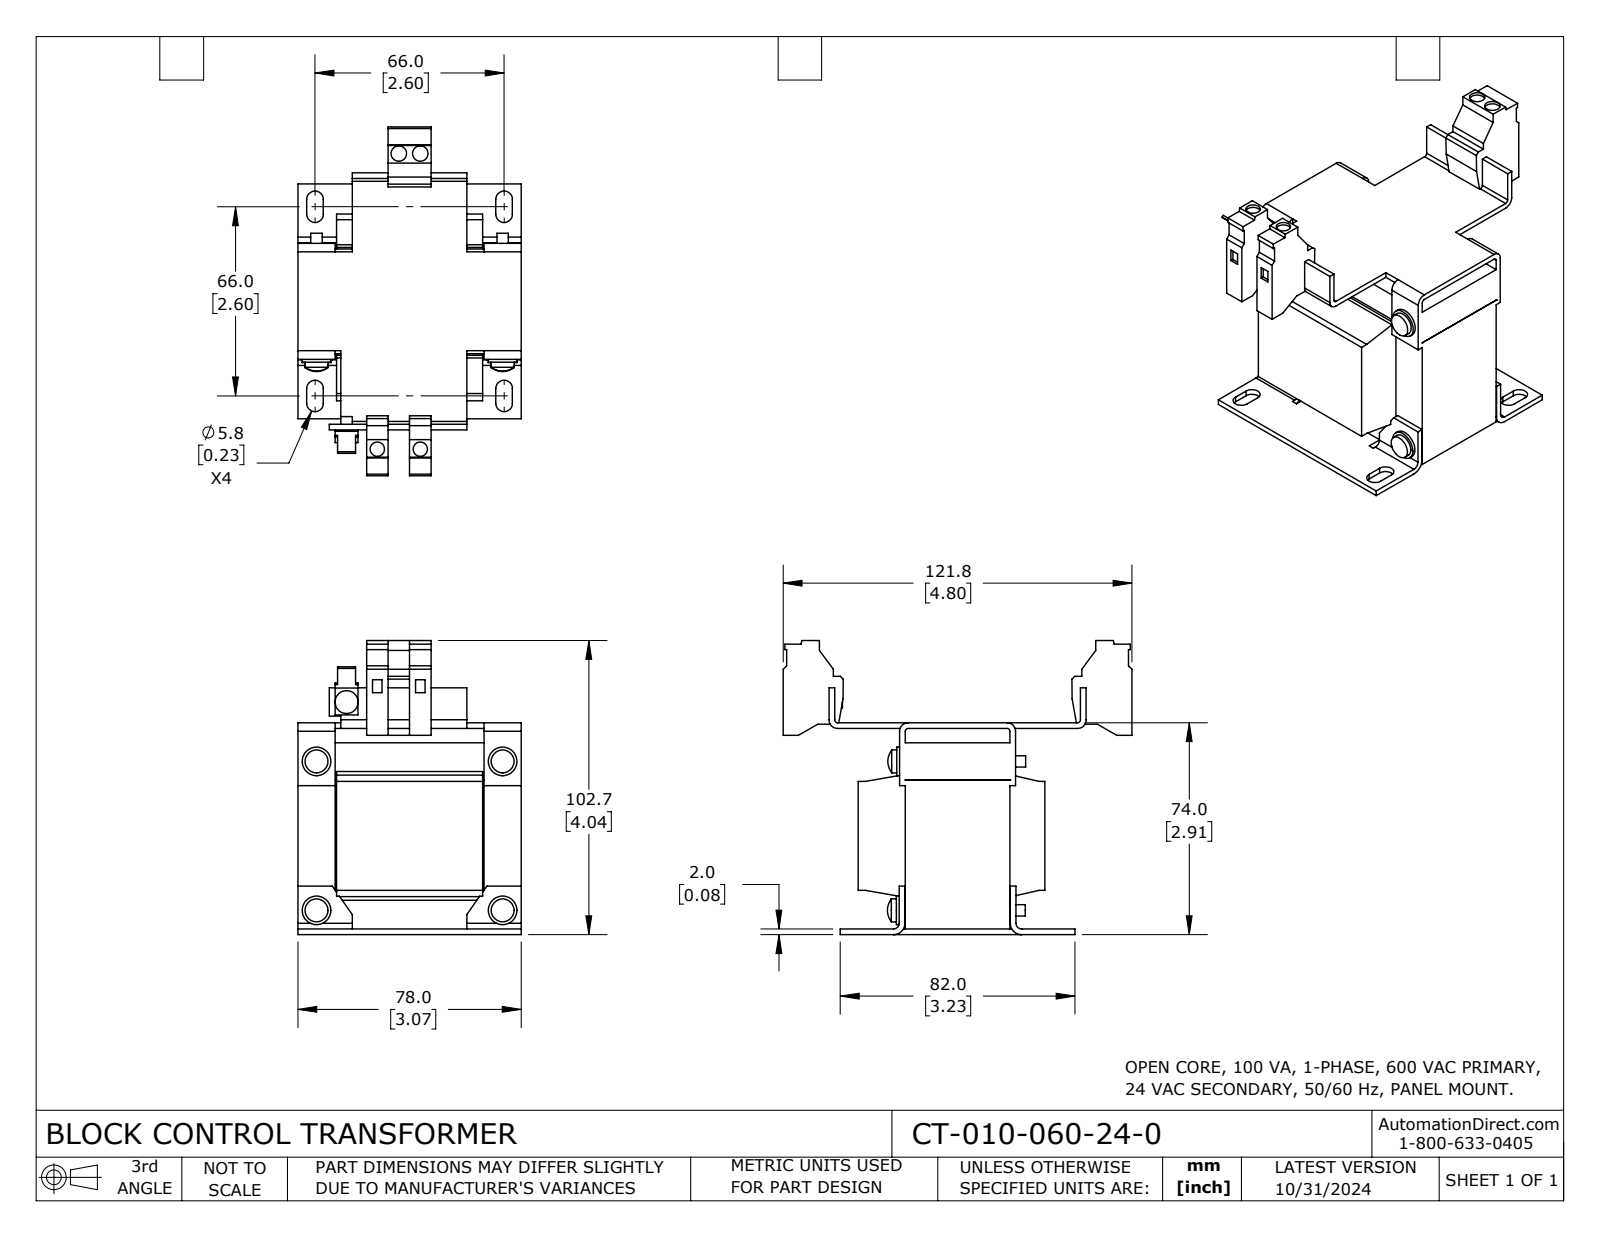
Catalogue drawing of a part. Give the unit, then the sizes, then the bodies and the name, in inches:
Units: inches
Overall size (bounding box): 4.795 × 4.043 × 3.071
Round holes (diameter × count): ⌀0.197 ×2, ⌀0.213 ×2
Round bosses / shafts (diameter × count): ⌀0.315 ×5, ⌀0.157 ×5, ⌀0.394 ×4, ⌀0.177 ×2
Partial cylindrical surfaces — rounded edges, fillets, slot ends (radius × count): R0.114 ×8, R0.039 ×4, R0.118 ×4, R0.079 ×2, R0.157 ×2
Main face-to-face distances: 0.079, 2.835, 0.709, 0.531, 2.047, 0.512, 2.559, 0.02, 2.028, 0.787
Hole centre spacings: 4.074, 0.295, 0.591, 4.063, 4.106
Volume: 17.31 in³ · Surface area: 106.1 in²
Bodies: 1 solid, 334 faces (253 planar, 77 cylindrical, 4 other)
Part name (STEP PRODUCT): CT-010-060-24-0
STEP written by: SolidWorks 2023 (CONFIG_CONTROL_DESIGN)
